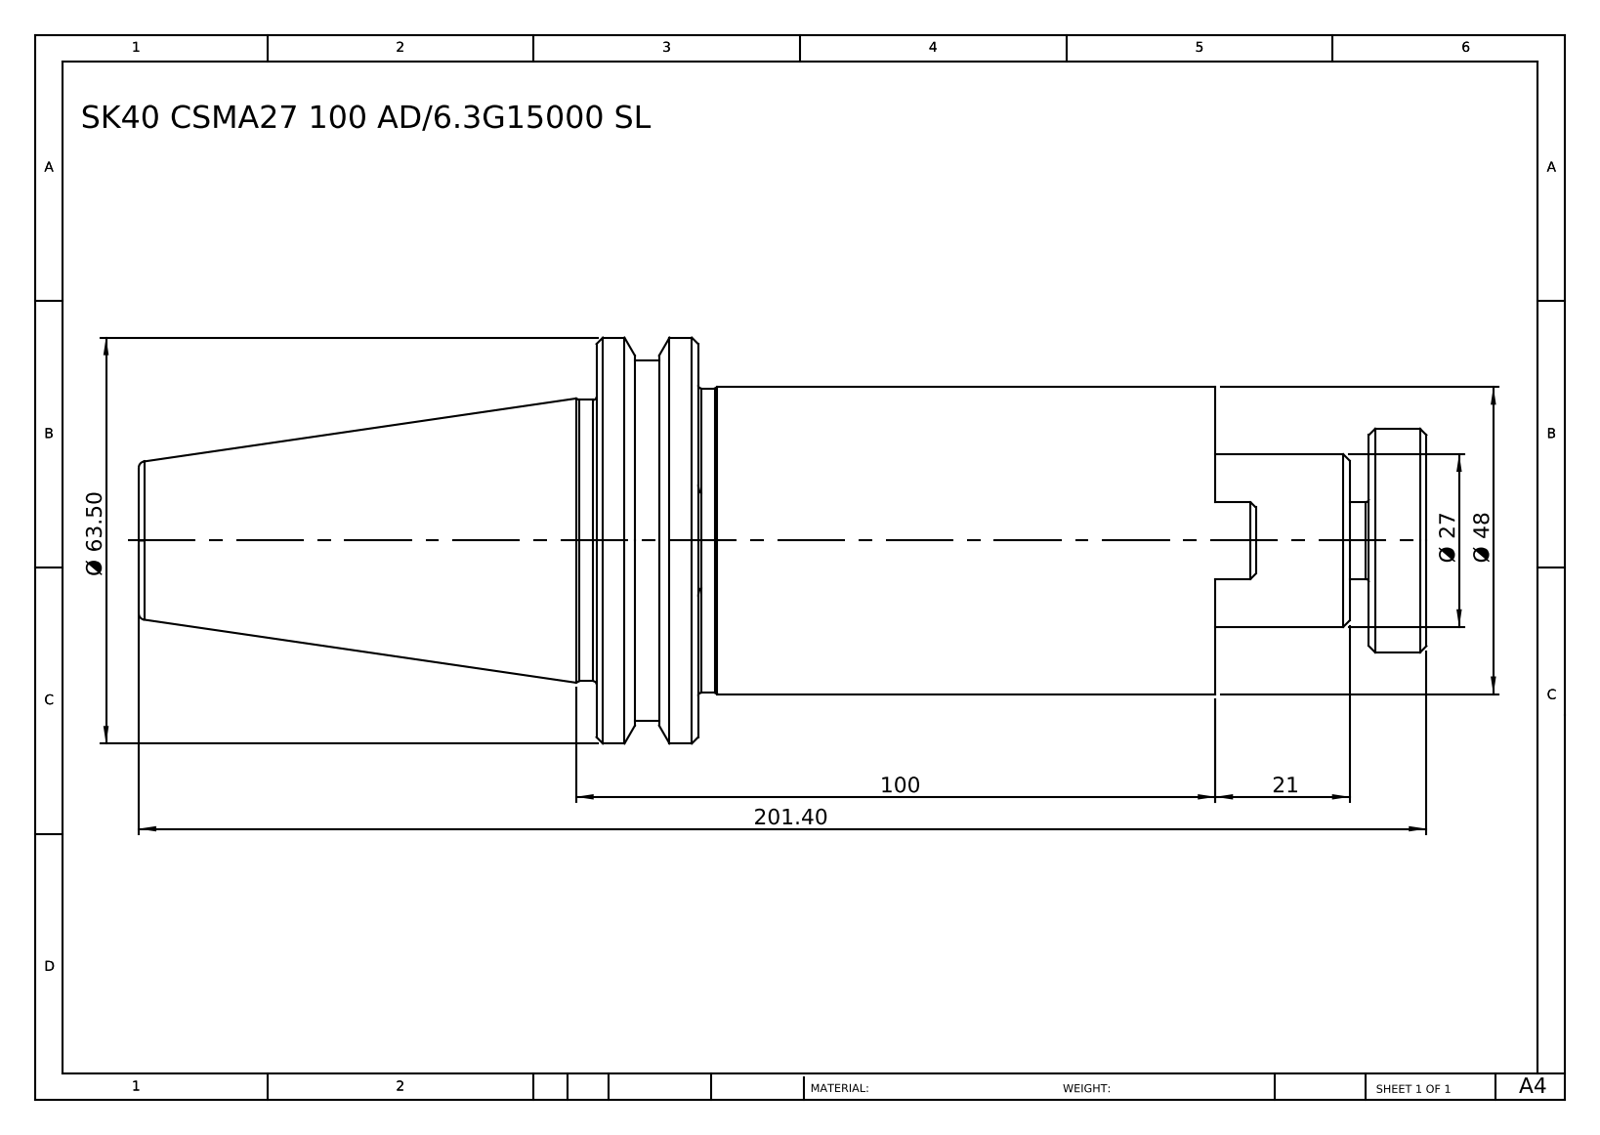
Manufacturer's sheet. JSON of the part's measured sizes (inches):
{"part_name": "SK 40 CSMA27 100 AD-6.3G15000 SL SP", "step_written_by": "SolidWorks 2014 (CONFIG_CONTROL_DESIGN)", "units": "inches", "bodies": {"solids": 1, "faces": 74, "planar": 19, "cylindrical": 20, "other": 35}, "overall_size": [7.929, 2.5, 2.5], "volume_in3": 17.43, "surface_area_in2": 52.67, "round_bosses_or_shafts": [[2.5, 1], [2.215, 1], [1.89, 1], [1.874, 1], [1.732, 1], [1.378, 1], [1.063, 1], [0.472, 1]], "partial_cylinders_radius": [[0.61, 1]], "face_to_face_distances": [0.626, 3.185, 3.811, 1.299, 4.484, 5.11, 0.354, 0.945, 4.13, 4.756]}
